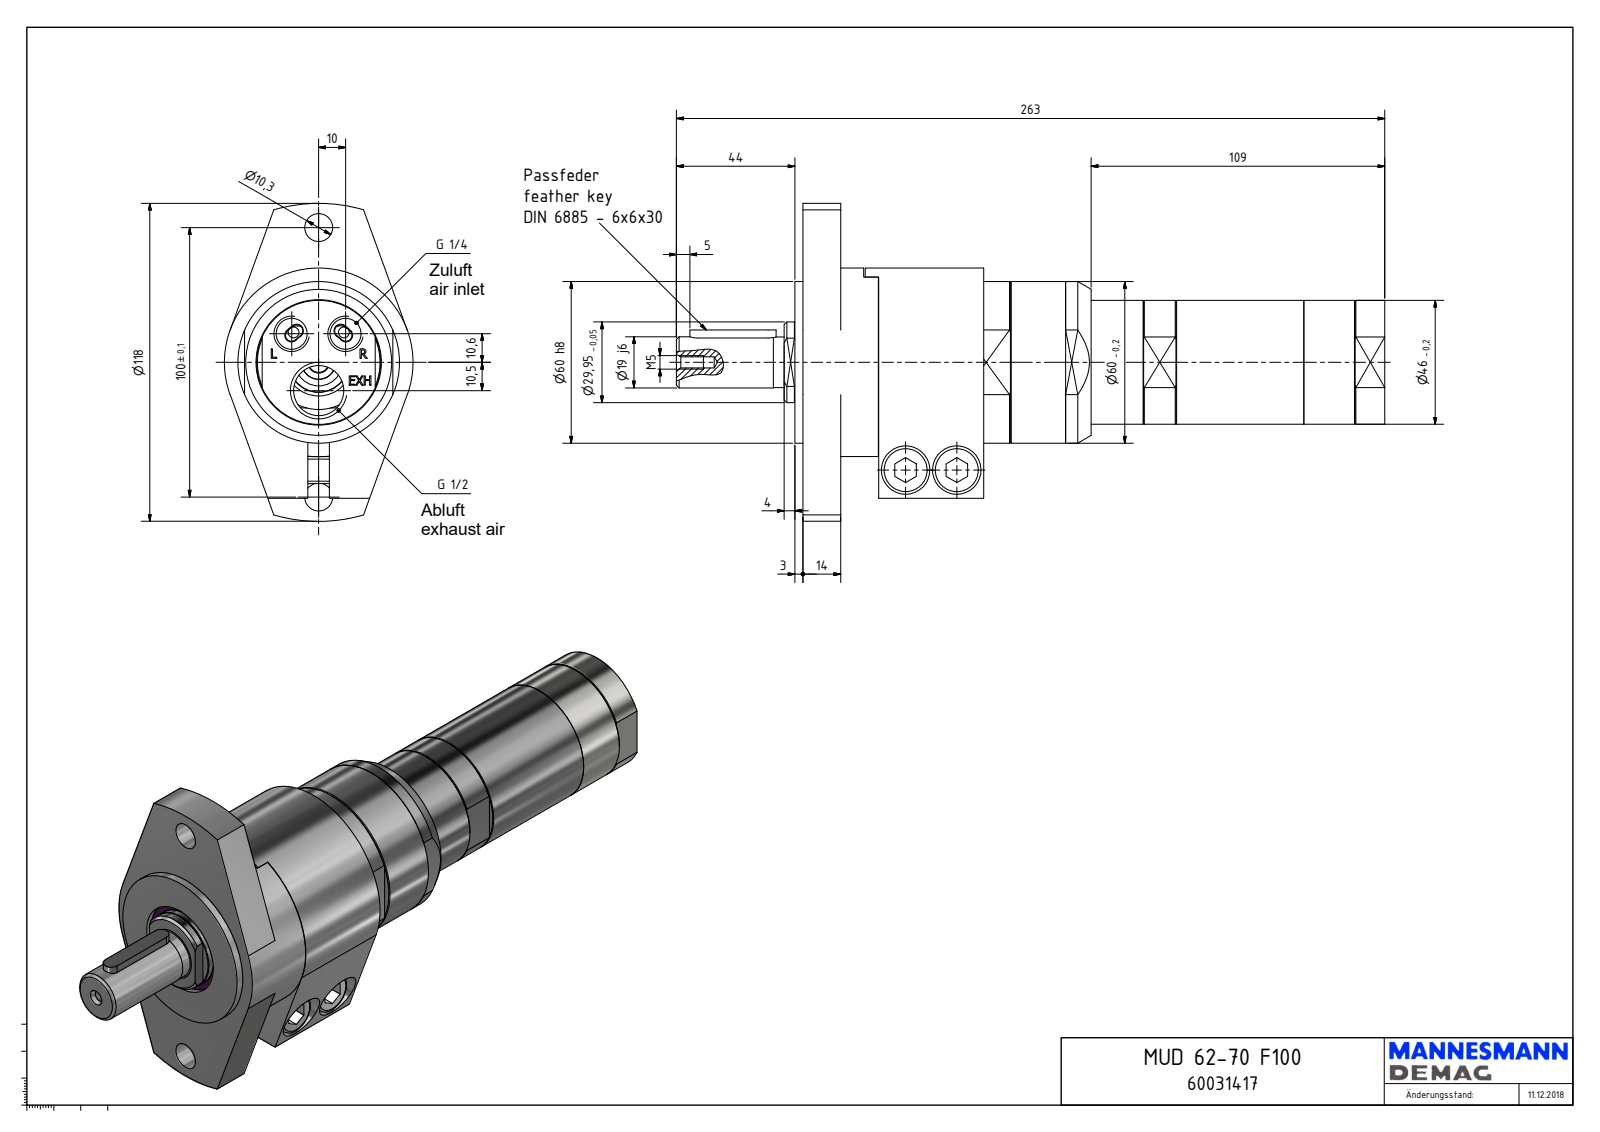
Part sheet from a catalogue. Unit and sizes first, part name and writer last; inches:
Units: inches
Overall size (bounding box): 10.354 × 4.646 × 2.756
Round holes (diameter × count): ⌀0.33 ×2, ⌀0.406 ×2, ⌀0.413 ×2, ⌀0.451 ×2, ⌀0.709 ×2, ⌀0.061 ×1, ⌀0.157 ×1, ⌀0.163 ×1, ⌀0.217 ×1, ⌀0.733 ×1, ⌀1.378 ×1, ⌀1.437 ×1
Round bosses / shafts (diameter × count): ⌀0.63 ×2, ⌀0.394 ×2, ⌀2.756 ×1, ⌀2.362 ×1, ⌀2.172 ×1, ⌀1.811 ×1, ⌀1.179 ×1, ⌀0.748 ×1
Partial cylindrical surfaces — rounded edges, fillets, slot ends (radius × count): R0.118 ×2, R0.197 ×2, R0.676 ×1, R0.748 ×1, R0.983 ×1, R2.323 ×1
Main face-to-face distances: 0.551, 0.669, 0.118, 2.76, 2.642, 2.091, 1.224, 1.106, 0.555, 1.535
Hole centre spacings: 0.574, 0.919, 1.6, 1.969, 2.418, 0.413, 0.748, 0.787
Volume: 37.81 in³ · Surface area: 117.1 in²
Bodies: 1 solid, 278 faces (157 planar, 65 cylindrical, 56 other)
Part name (STEP PRODUCT): MUD 62-70 F100_60031417
STEP written by: Autodesk Inventor 2018 (AUTOMOTIVE_DESIGN)
